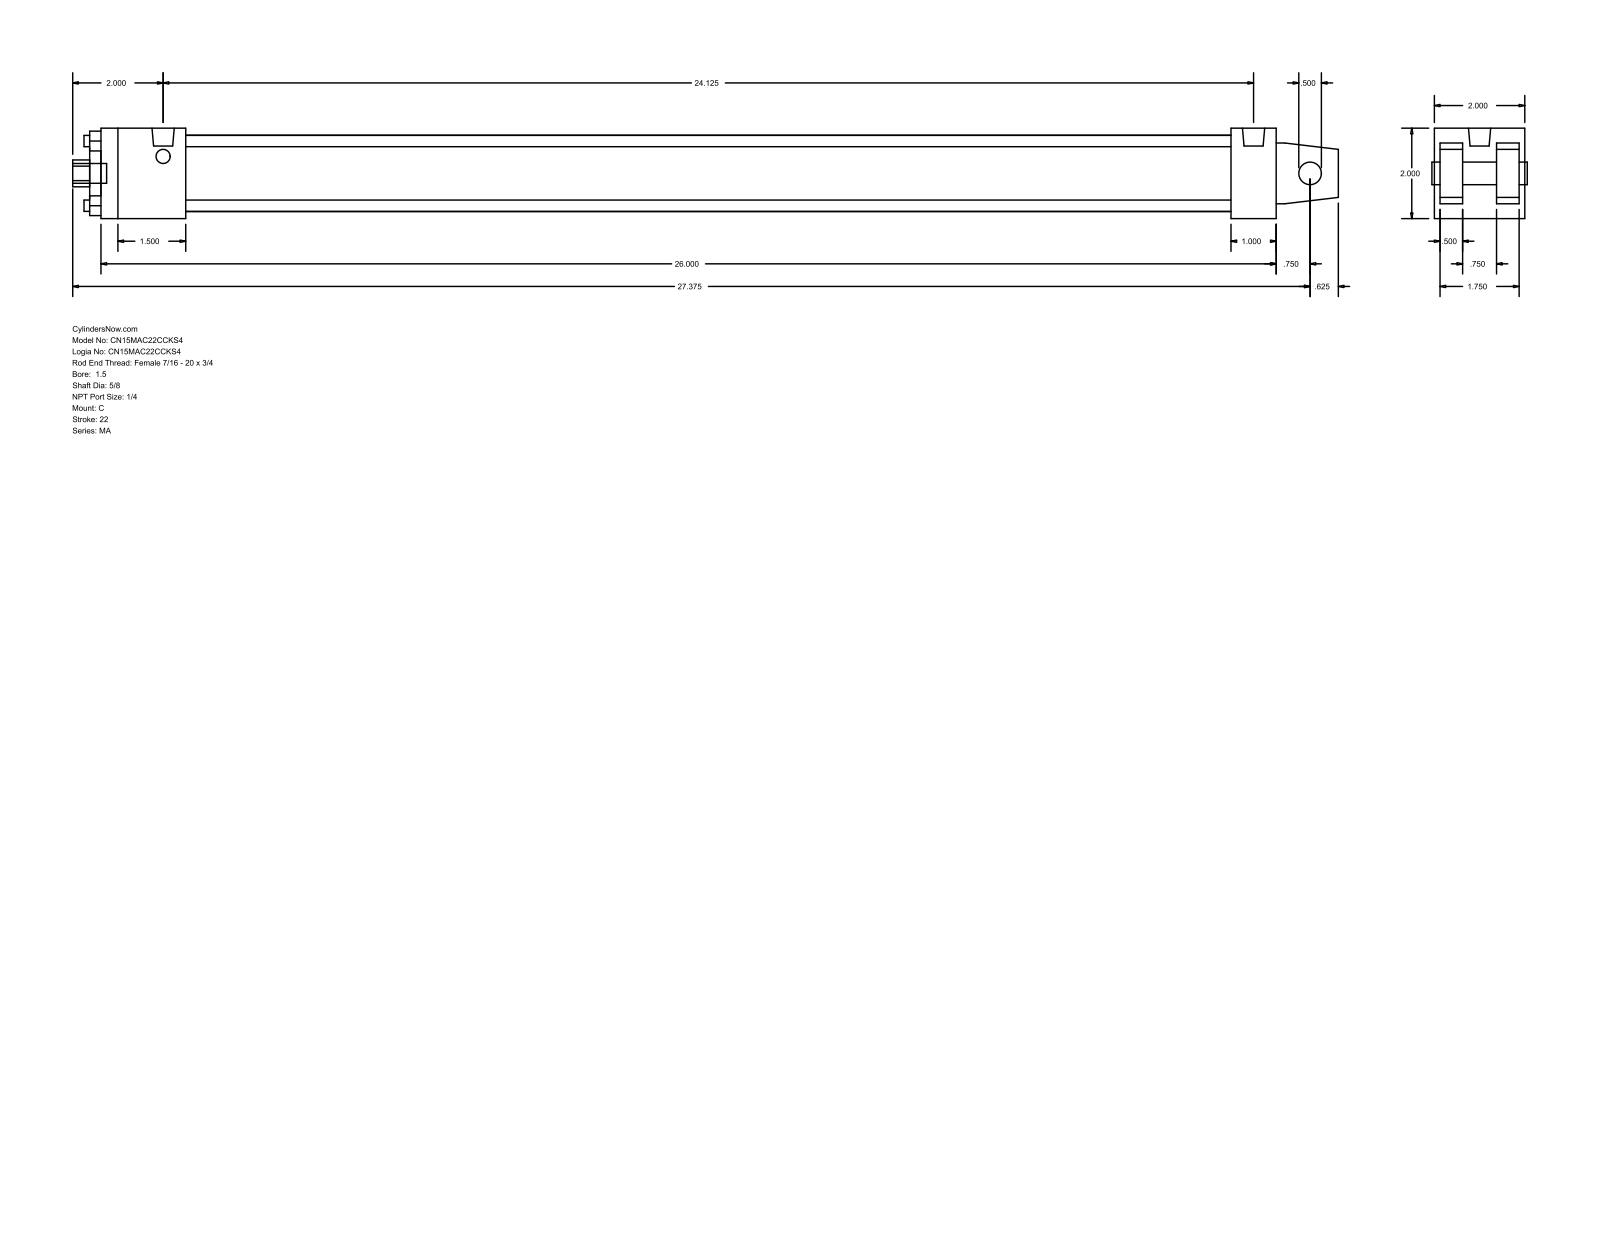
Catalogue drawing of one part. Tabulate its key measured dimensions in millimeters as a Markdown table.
| quantity | value |
| --- | --- |
| part name | MA_C__0150_0.625 |
| STEP written by | GSSL Pune (CONFIG_CONTROL_DESIGN) |
| units | millimeters |
| bodies | 0 solids, 103 faces (76 planar, 27 cylindrical, 0 other) |
| overall size | 711.2 × 50.8 × 50.8 |
| round holes (diameter × count) | 6.35 × 4, 12.7 × 1, 15.88 × 1, 28.57 × 1, 42.93 × 1 |
| round bosses / shafts (diameter × count) | 7.94 × 4, 12.49 × 2, 11.11 × 1 |
| partial cylindrical surfaces (radius × count) | 7.54 × 1 |
| main face-to-face distances | 50.8, 34.93, 12.7, 3.17, 15.87, 47.63, 31.76, 660.39, 635, 25.39 |
| hole center spacings | 25.68, 36.32, 51.36 |
